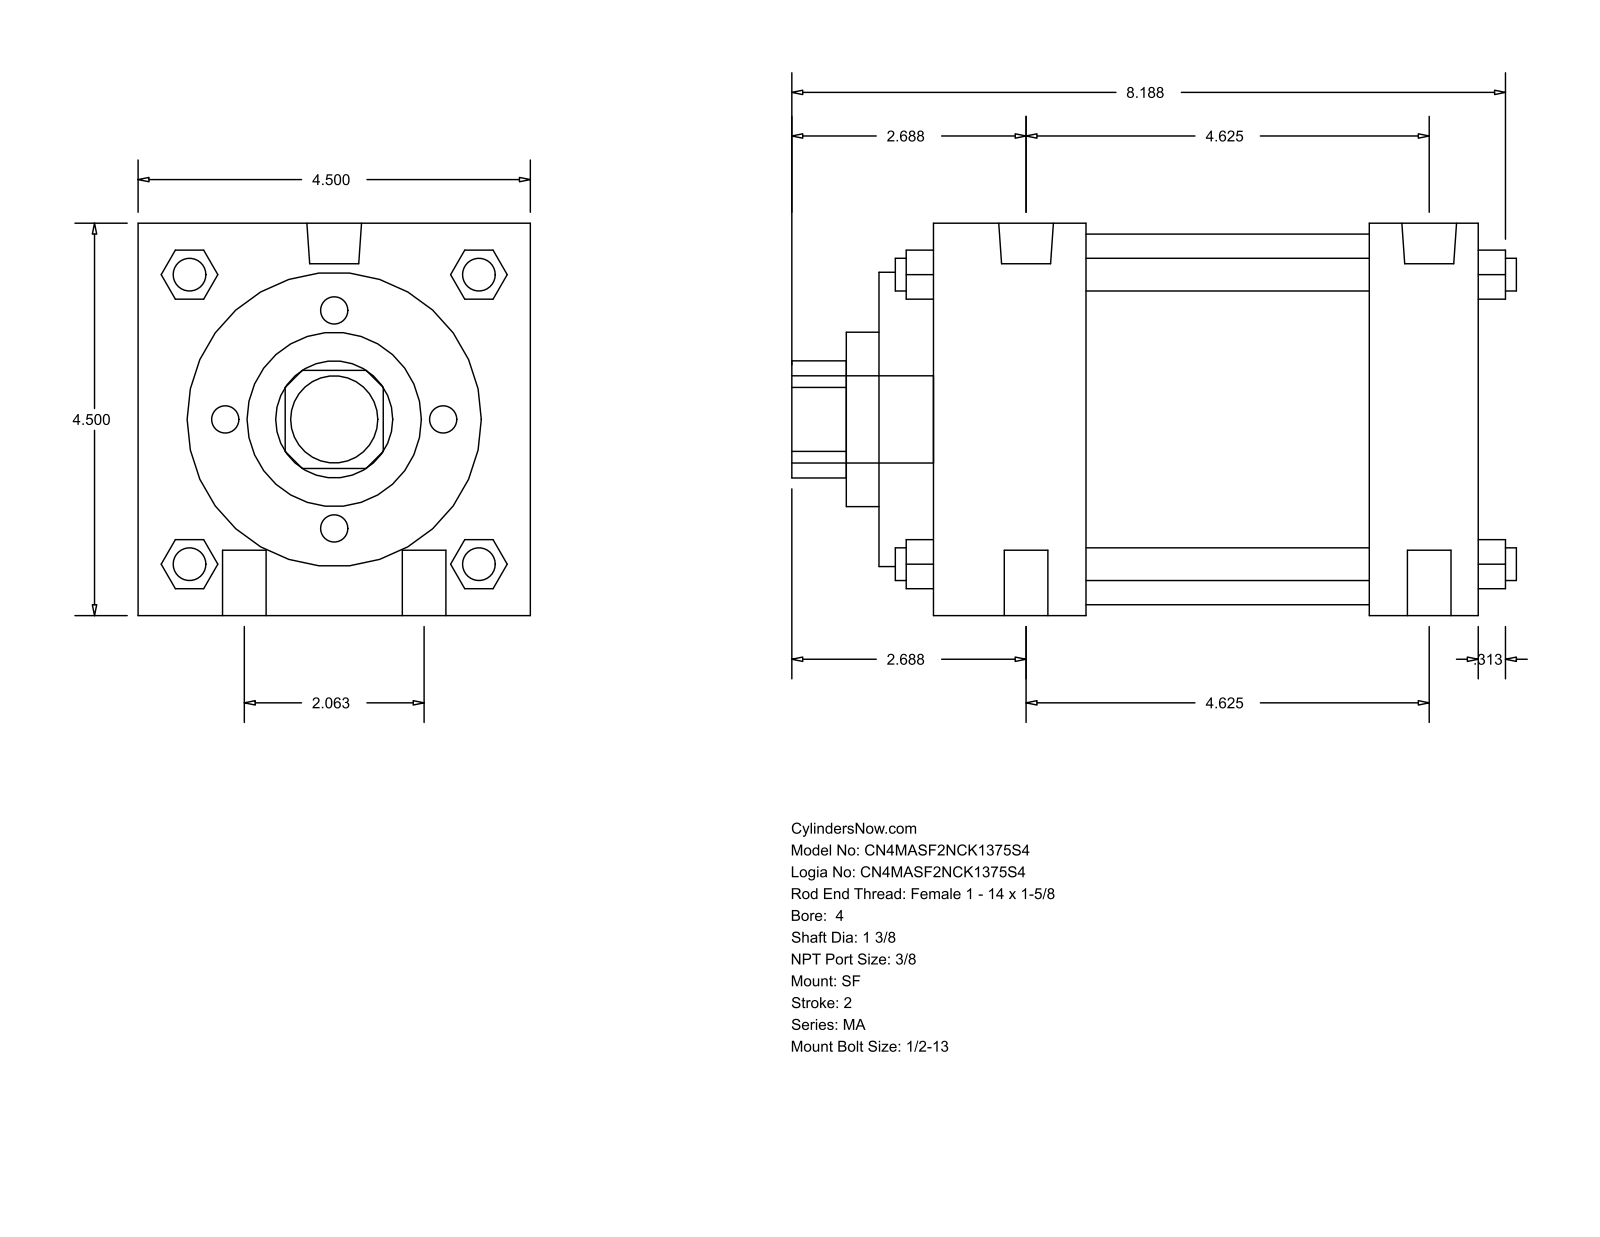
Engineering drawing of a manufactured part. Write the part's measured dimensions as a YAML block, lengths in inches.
part_name: "MA_SF__0400_1.375"
step_written_by: "GSSL Pune (CONFIG_CONTROL_DESIGN)"
units: inches
bodies: {solids: 0, faces: 126, planar: 95, cylindrical: 31, other: 0}
overall_size: [8.313, 4.5, 4.5]
round_holes:
  - {diameter: 1.375, count: 1}
  - {diameter: 2, count: 1}
  - {diameter: 3.375, count: 1}
  - {diameter: 4.25, count: 1}
round_bosses_or_shafts:
  - {diameter: 0.5, count: 4}
  - {diameter: 0.375, count: 4}
  - {diameter: 0.627, count: 2}
  - {diameter: 0.437, count: 2}
  - {diameter: 1, count: 1}
partial_cylinders:
  - {radius: 0.672, count: 1}
face_to_face_distances: [4.5, 6.25, 0.625, 6.875, 5.625, 5, 1.25, 2.375, 1.75, 3.25]
